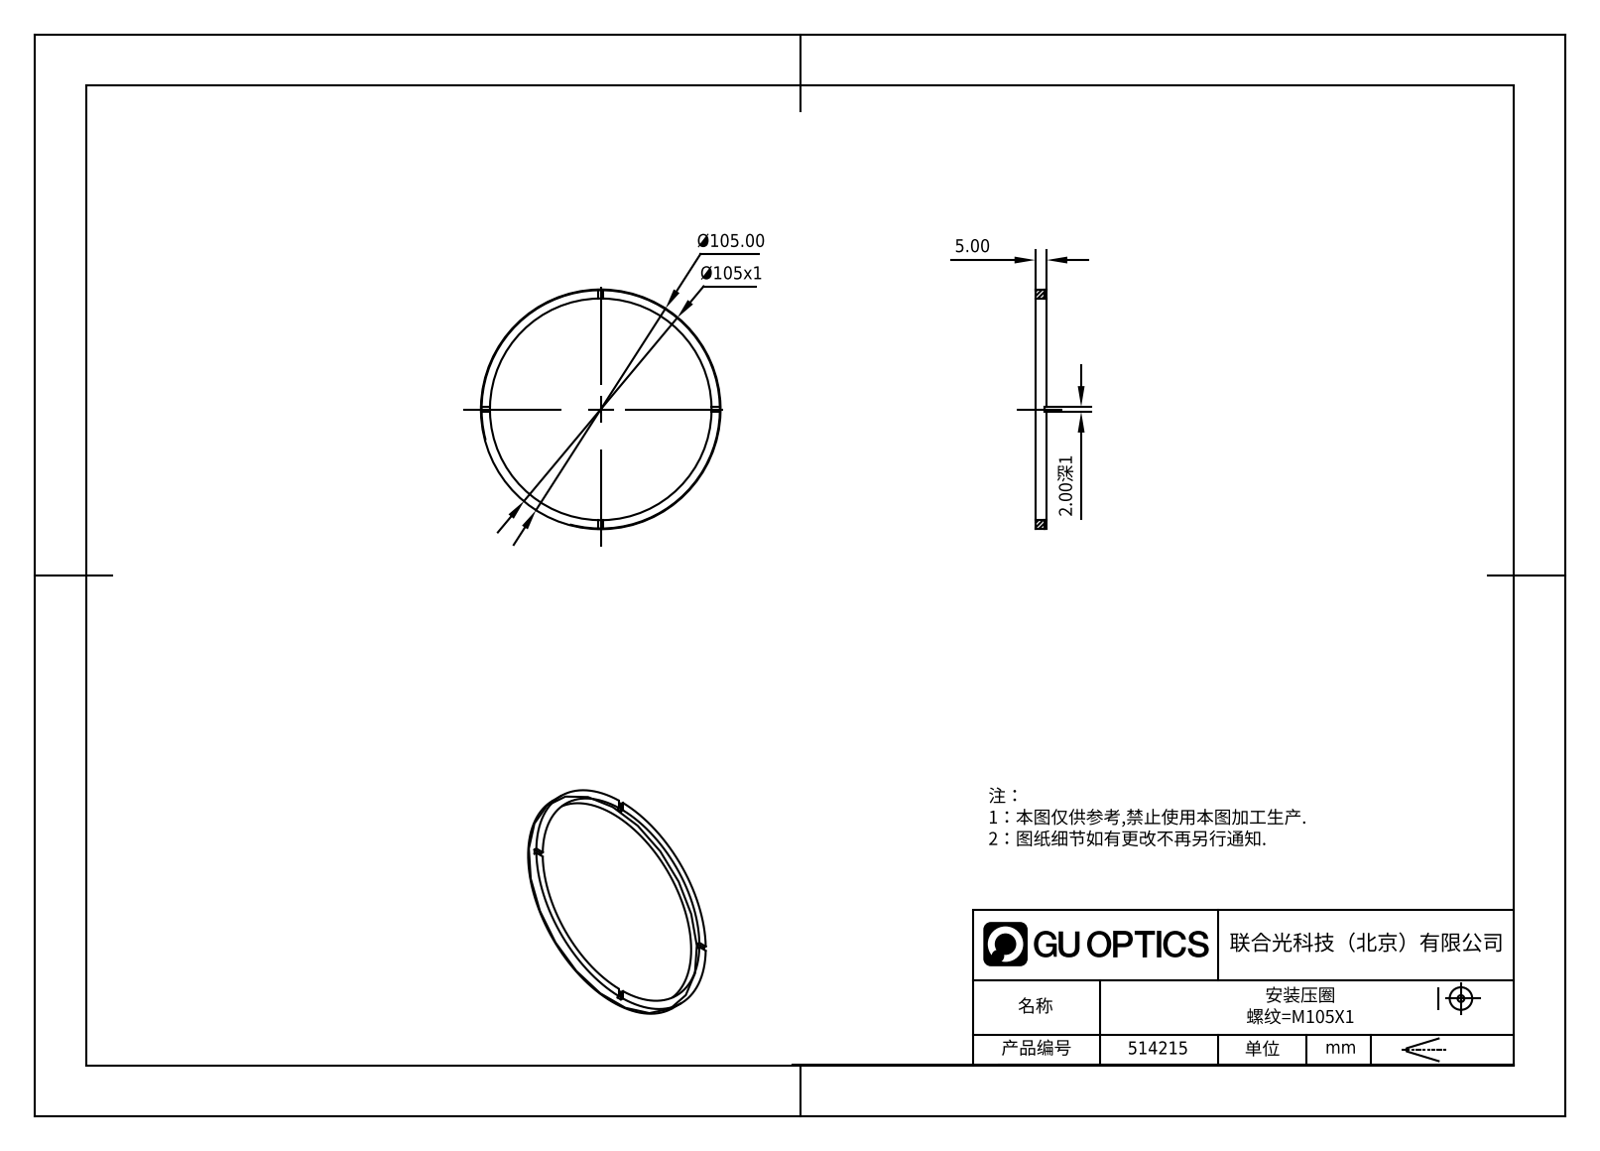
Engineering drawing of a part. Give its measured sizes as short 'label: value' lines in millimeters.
name: 514215
written by: SolidWorks 2020 (CONFIG_CONTROL_DESIGN)
unit: mm
bodies: 1 solid, 21 faces (17 planar, 4 cylindrical, 0 other)
size: 105 × 105 × 5
volume: 6 314 mm³; area: 5 727 mm²
holes: 1× ⌀97
bosses: 1× ⌀105
face distances: 5, 4, 1, 2
